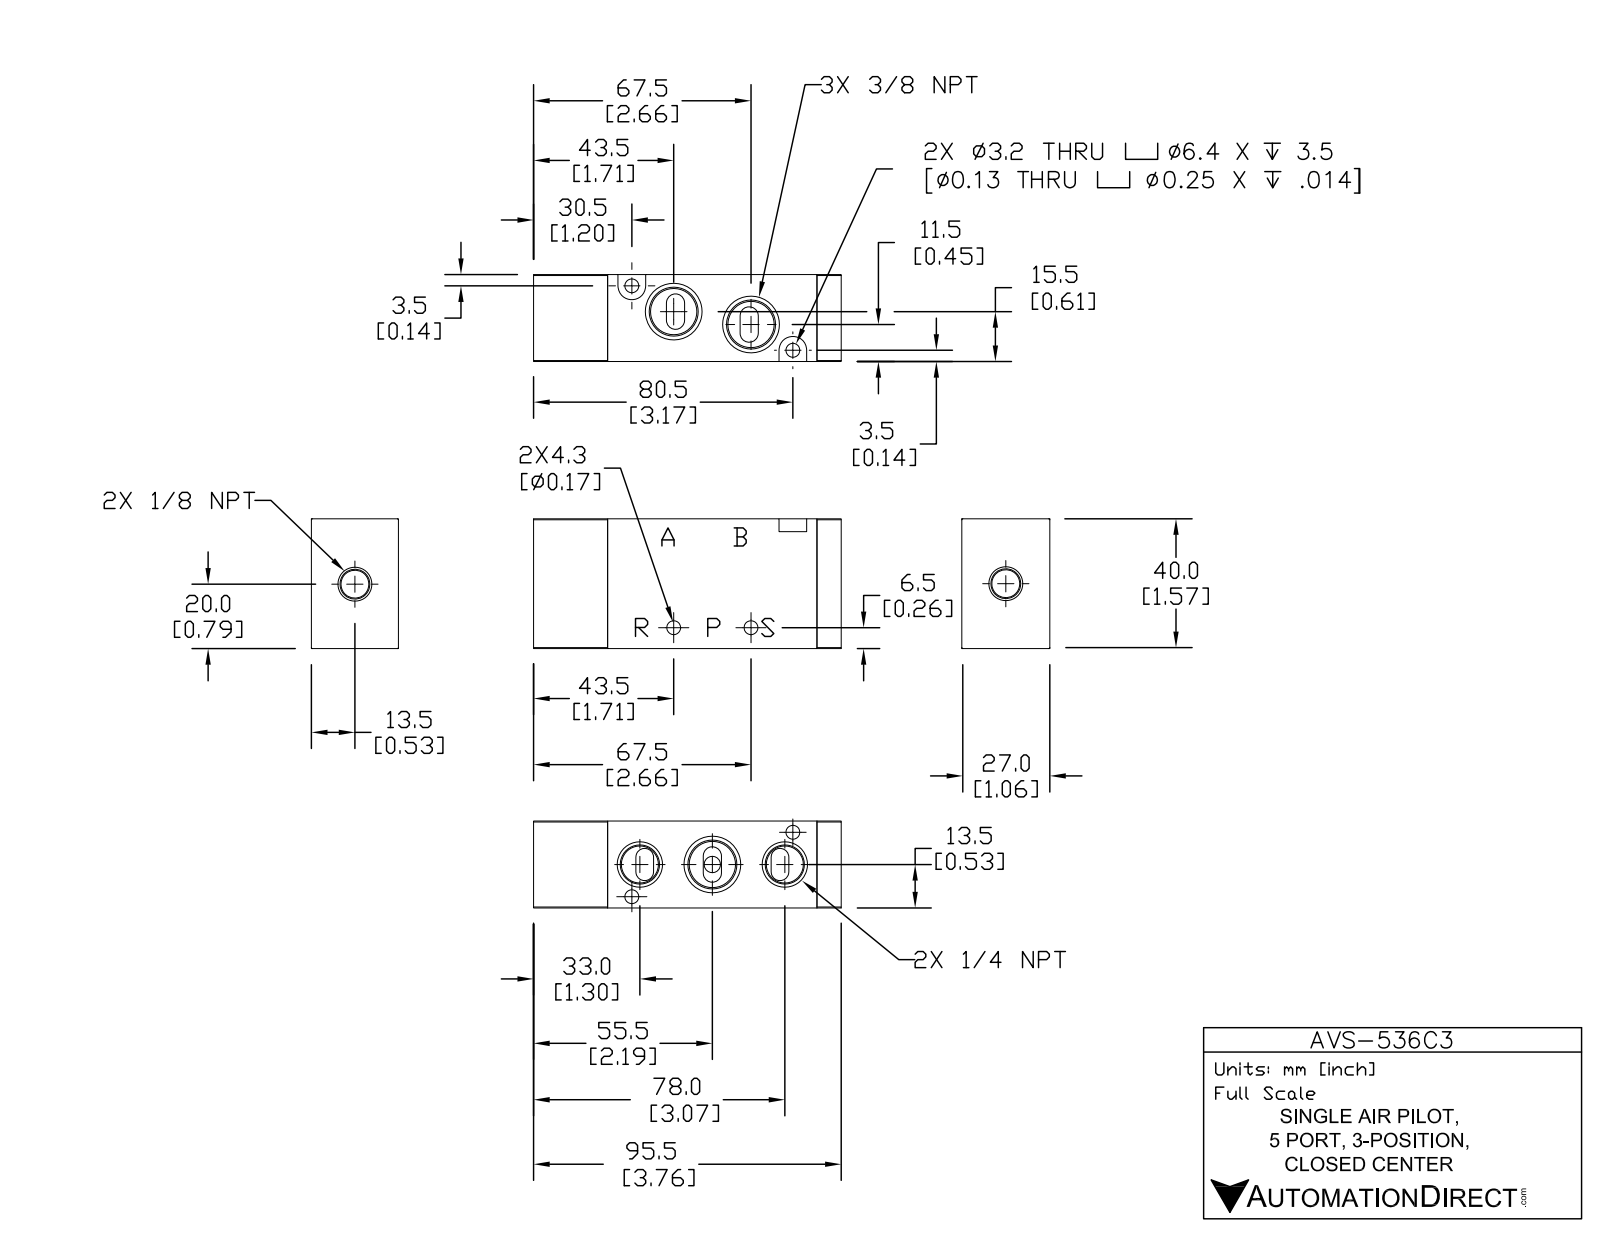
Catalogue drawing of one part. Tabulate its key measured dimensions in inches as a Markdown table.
| quantity | value |
| --- | --- |
| part name | AVS-536C3 |
| STEP written by | SolidWorks 2015 (CONFIG_CONTROL_DESIGN) |
| units | inches |
| bodies | 3 solids, 111 faces (47 planar, 36 cylindrical, 28 other) |
| overall size | 5.118 × 1.575 × 1.063 |
| volume | 7.873 in³ |
| surface area | 44.6 in² |
| round holes (diameter × count) | 0.169 × 4, 0.199 × 1 |
| partial cylindrical surfaces (radius × count) | 0.111 × 6, 0.012 × 4, 0.108 × 4, 0.169 × 2 |
| main face-to-face distances | 1.063, 1.575, 3.307, 0.906, 4.213, 5.118, 0.63, 0.461, 1.114, 0.945 |
| hole center spacings | 1.06, 0.945, 2.12 |
